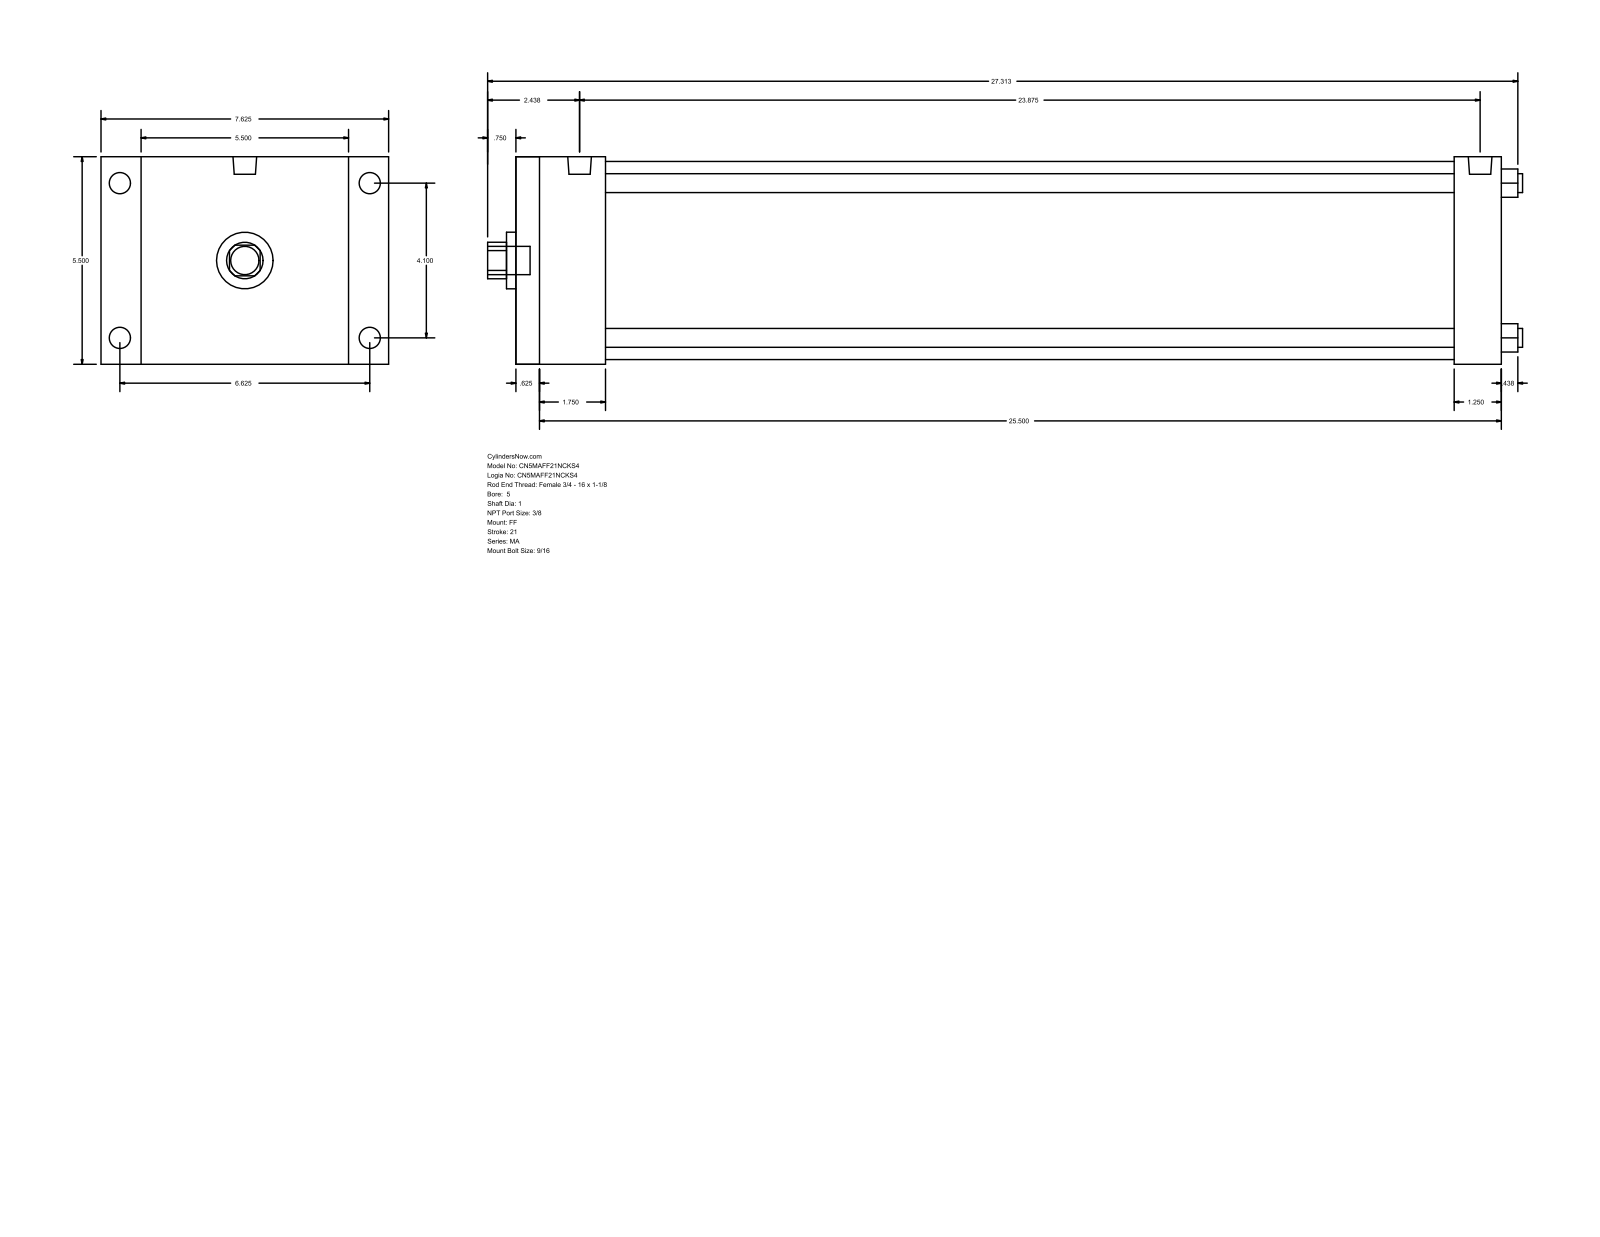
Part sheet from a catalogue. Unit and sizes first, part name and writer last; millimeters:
Units: millimetres
Overall size (bounding box): 696.91 × 193.68 × 139.7
Round holes (diameter × count): ⌀12.7 ×4, ⌀25.4 ×1, ⌀38.1 ×1, ⌀133.35 ×1
Round bosses / shafts (diameter × count): ⌀14.29 ×4, ⌀11.11 ×4, ⌀15.93 ×2, ⌀19.05 ×1
Partial cylindrical surfaces — rounded edges, fillets, slot ends (radius × count): R12.29 ×1
Main face-to-face distances: 139.7, 663.57, 15.87, 647.7, 631.83, 615.96, 31.74, 60.33, 44.46, 571.5
Hole centre spacings: 73.64, 104.14, 147.28
Bodies: 0 solids, 92 faces (64 planar, 28 cylindrical, 0 other)
Part name (STEP PRODUCT): MA_FF__0500_1
STEP written by: GSSL Pune (CONFIG_CONTROL_DESIGN)
